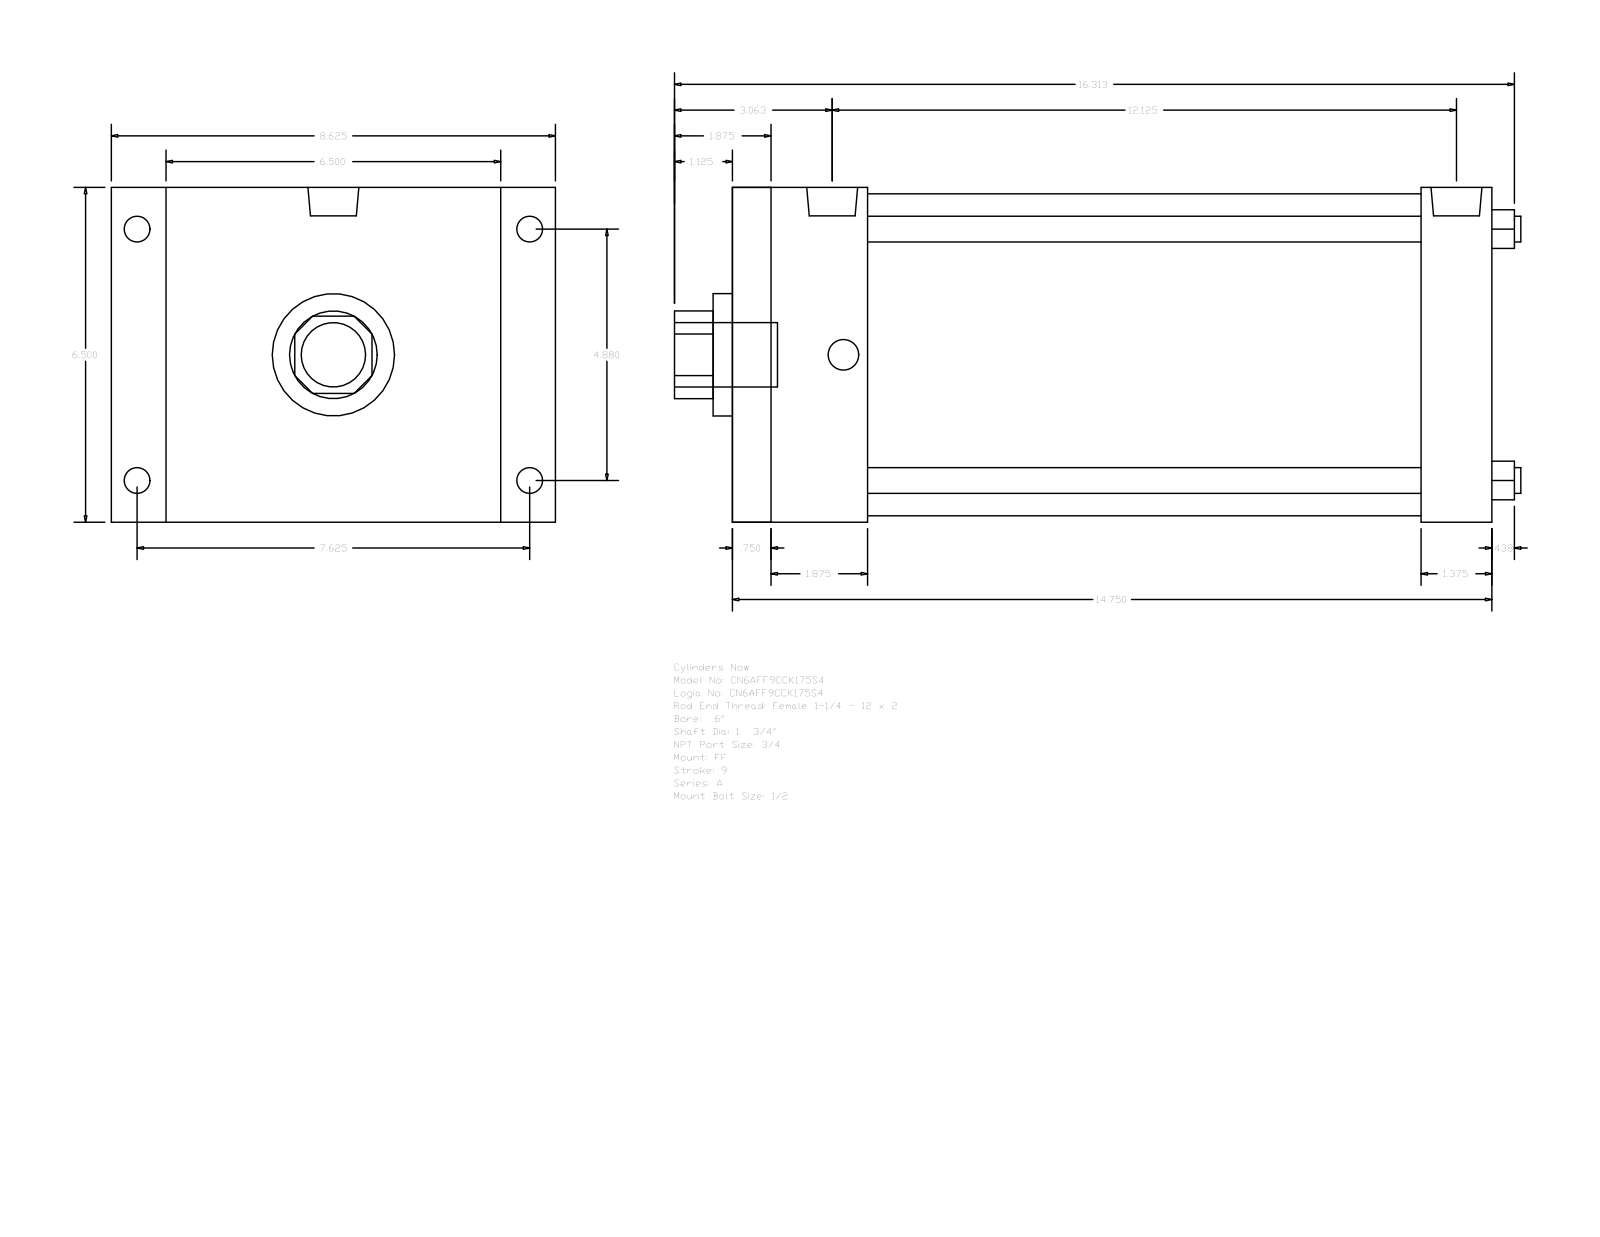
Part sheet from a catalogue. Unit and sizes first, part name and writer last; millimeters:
Units: millimetres
Overall size (bounding box): 417.51 × 219.07 × 165.1
Round holes (diameter × count): ⌀12.7 ×4, ⌀44.45 ×1, ⌀60.33 ×1, ⌀158.75 ×1
Round bosses / shafts (diameter × count): ⌀15.08 ×4, ⌀12.7 ×4, ⌀25.12 ×2, ⌀31.75 ×1
Partial cylindrical surfaces — rounded edges, fillets, slot ends (radius × count): R21.63 ×1
Main face-to-face distances: 165.1, 374.66, 19.05, 355.61, 66.68, 47.63, 307.98, 339.73, 320.68, 273.05
Hole centre spacings: 87.65, 123.96, 175.31
Bodies: 0 solids, 92 faces (64 planar, 28 cylindrical, 0 other)
Part name (STEP PRODUCT): A_FF__0600_1.75
STEP written by: GSSL Pune (CONFIG_CONTROL_DESIGN)
